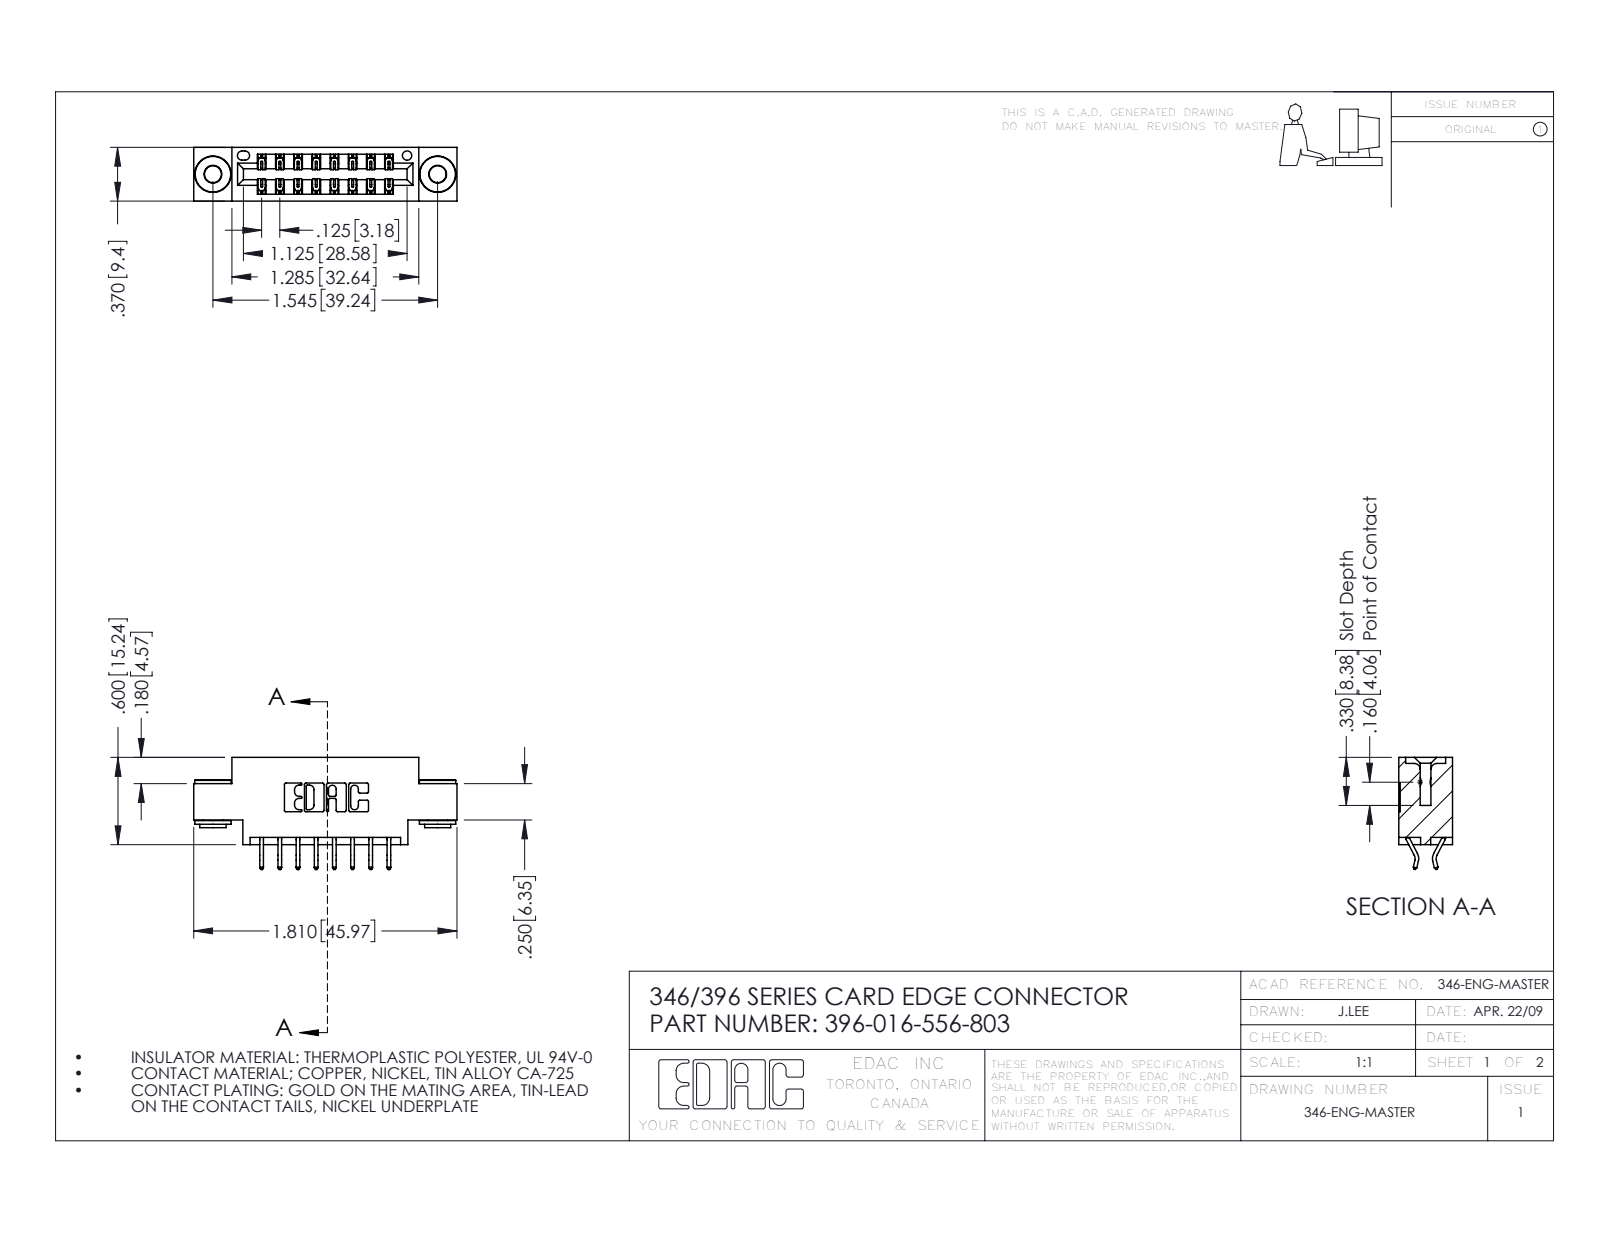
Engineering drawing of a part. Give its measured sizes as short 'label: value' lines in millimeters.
name: 345-250-002_345-250-002-102; 345-292-001_556 Tail; 346 Part_0.170 Offset - 0.156 Dia-TH; 396-016-556-803
written by: SolidWorks 2016 (CONFIG_CONTROL_DESIGN)
unit: mm
bodies: 19 solids, 1092 faces (714 planar, 370 cylindrical, 8 other)
size: 46 × 19.6 × 9.4
volume: 4 080 mm³; area: 5 457 mm²
holes: 2× ⌀2.9, 2× ⌀4, 1× ⌀1.6
bosses: 2× ⌀6.4, 2× ⌀4.6, 2× ⌀3.5
rounds: 24× R0.2, 22× R0.3, 6× R0.2, 6× R0.8, 3× R0.7, 2× R0.3, 2× R0.4, 2× R0.6
face distances: 6.4, 9.4, 1.2, 8.2, 0.6, 7, 3.8, 5.6, 2.5, 4.4
hole spacings: 6.2, 34.1, 39.2
